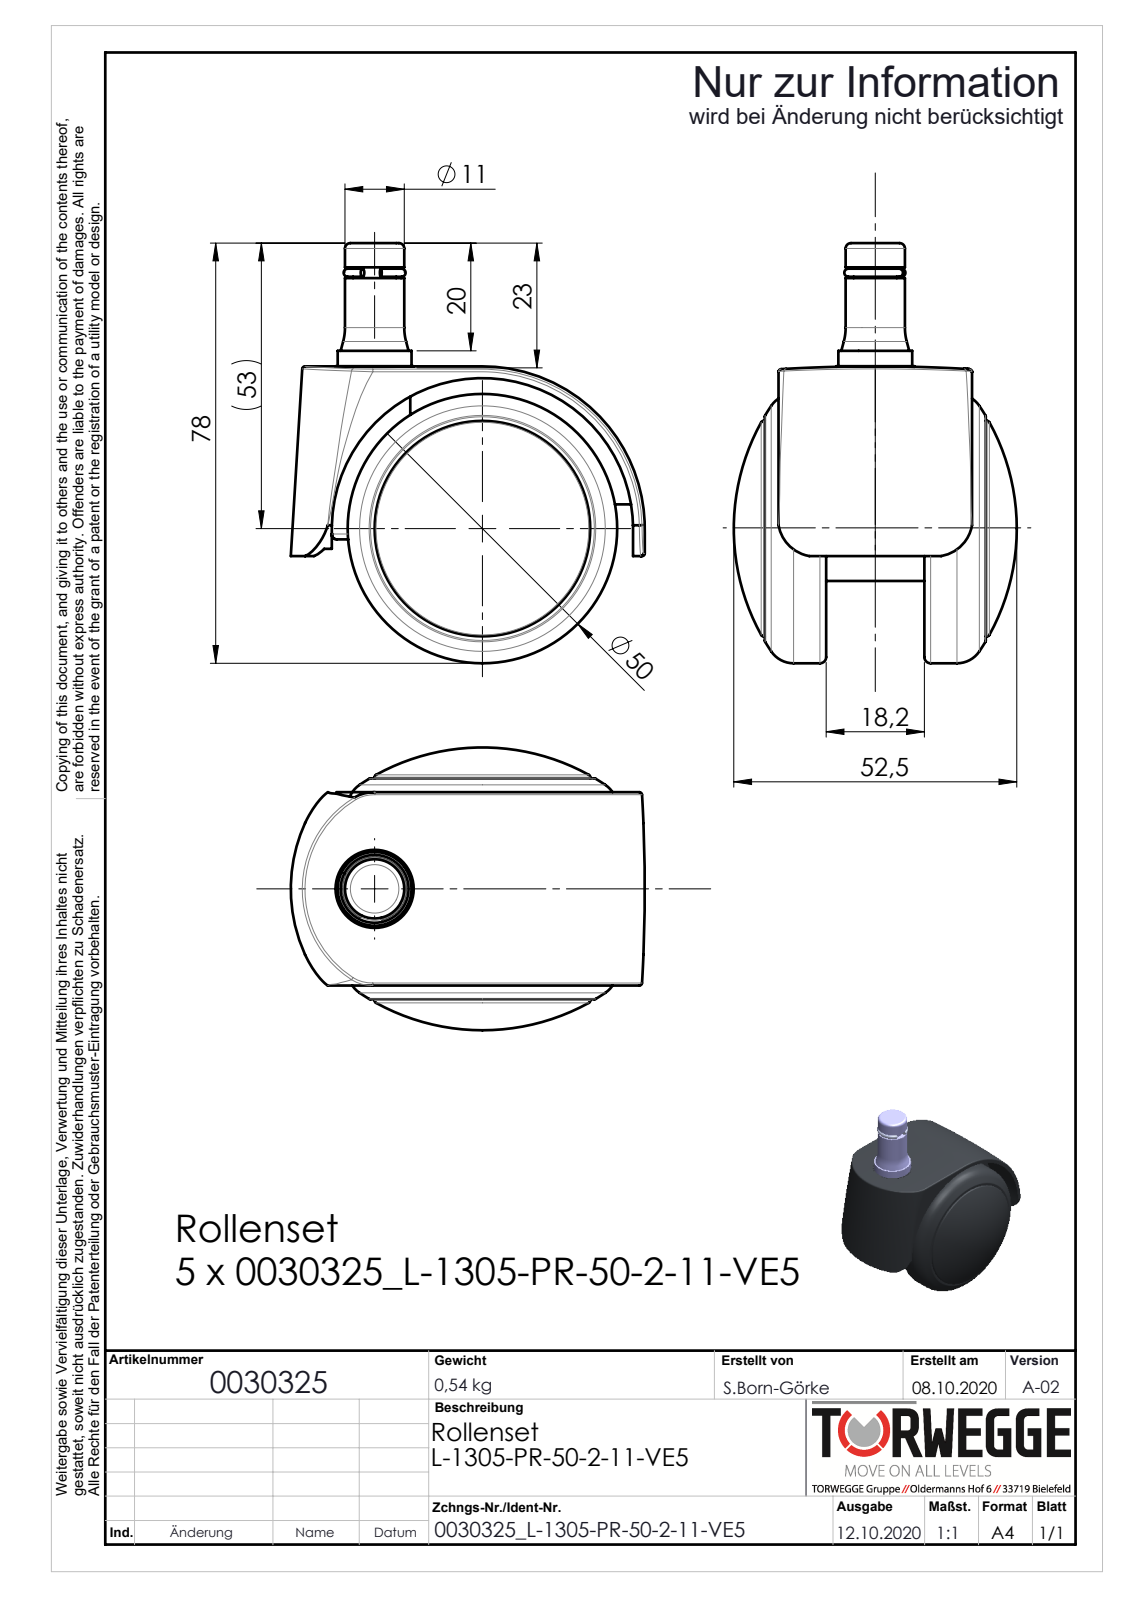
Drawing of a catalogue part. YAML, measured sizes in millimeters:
part_name: "0030325"
step_written_by: "SolidWorks 2018 (AUTOMOTIVE_DESIGN)"
units: millimeters
bodies: {solids: 3, faces: 179, planar: 51, cylindrical: 50, other: 78}
overall_size: [78, 65.67, 52.5]
volume: 77353
surface_area: 27818
round_holes:
  - {diameter: 3, count: 1}
  - {diameter: 8, count: 1}
  - {diameter: 10.2, count: 1}
round_bosses_or_shafts:
  - {diameter: 50, count: 1}
  - {diameter: 40, count: 1}
  - {diameter: 14.5, count: 1}
  - {diameter: 14.1, count: 1}
  - {diameter: 13.7, count: 1}
  - {diameter: 11, count: 1}
  - {diameter: 10, count: 1}
  - {diameter: 8.5, count: 1}
partial_cylinders:
  - {radius: 7, count: 2}
  - {radius: 3.5, count: 1}
  - {radius: 5, count: 1}
  - {radius: 8, count: 1}
  - {radius: 8.35, count: 1}
  - {radius: 8.55, count: 1}
  - {radius: 10.45, count: 1}
  - {radius: 29.62, count: 1}
face_to_face_distances: [4.61, 9, 13.61, 1.5, 13.45, 22.45, 11.95, 23.95, 10.5, 2.64]
